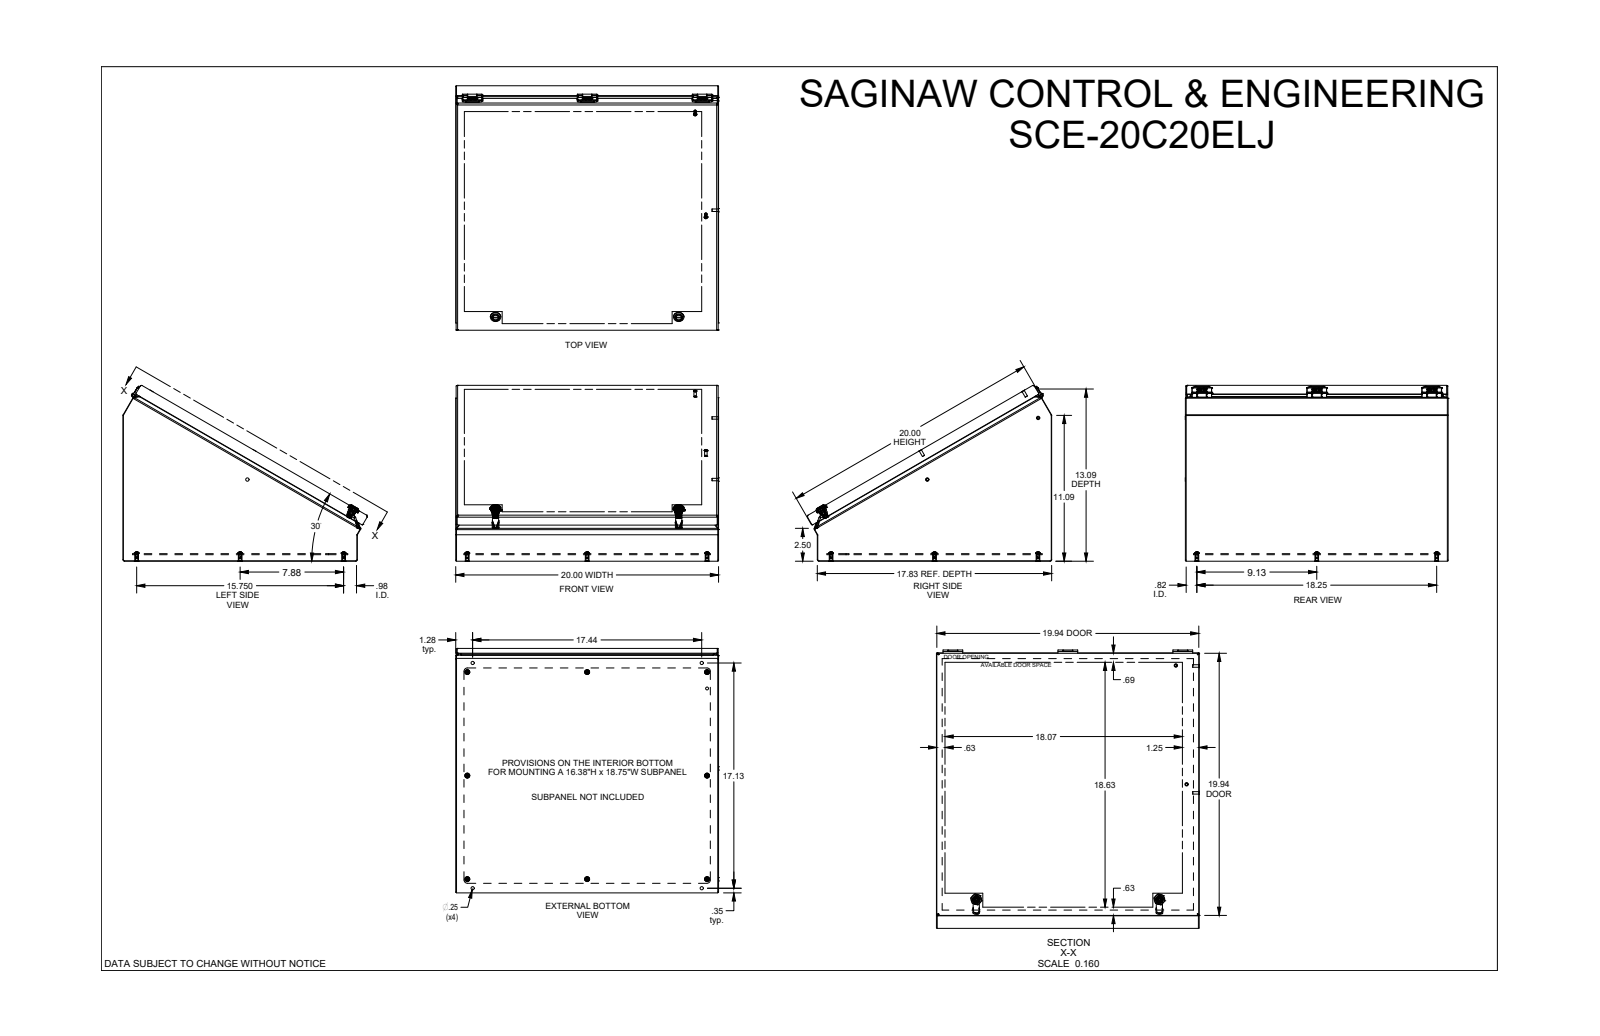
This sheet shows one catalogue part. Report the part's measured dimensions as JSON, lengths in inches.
{"part_name": "SCE-20C20ELJ", "step_written_by": "SolidWorks 2019 (AUTOMOTIVE_DESIGN)", "units": "inches", "bodies": {"solids": 39, "faces": 1412, "planar": 555, "cylindrical": 573, "other": 284}, "overall_size": [20.004, 18.594, 13.38], "volume_in3": 117.5, "surface_area_in2": 3690, "round_holes": [[0.25, 12], [0.19, 8], [0.281, 8], [0.193, 4], [0.02, 3], [0.1, 3], [0.174, 3], [0.266, 3], [0.2, 2], [0.239, 2], [0.254, 2], [0.269, 2]], "round_bosses_or_shafts": [[0.28, 8], [0.256, 4], [0.188, 4], [0.26, 3], [0.18, 3], [0.788, 2], [0.548, 2], [0.46, 2]], "partial_cylinders_radius": [[0.03, 36], [0.013, 31], [0.06, 24], [0.01, 22], [0.015, 22], [0.12, 16], [0.02, 13], [0.062, 9]], "face_to_face_distances": [0.06, 0.06, 0.436, 0.075, 0.496, 0.511, 0.571, 19.94, 19.88, 20], "hole_center_spacings": [8.75, 17.5, 0.802, 7.875, 8.576, 8.746, 9.125, 12.053]}
